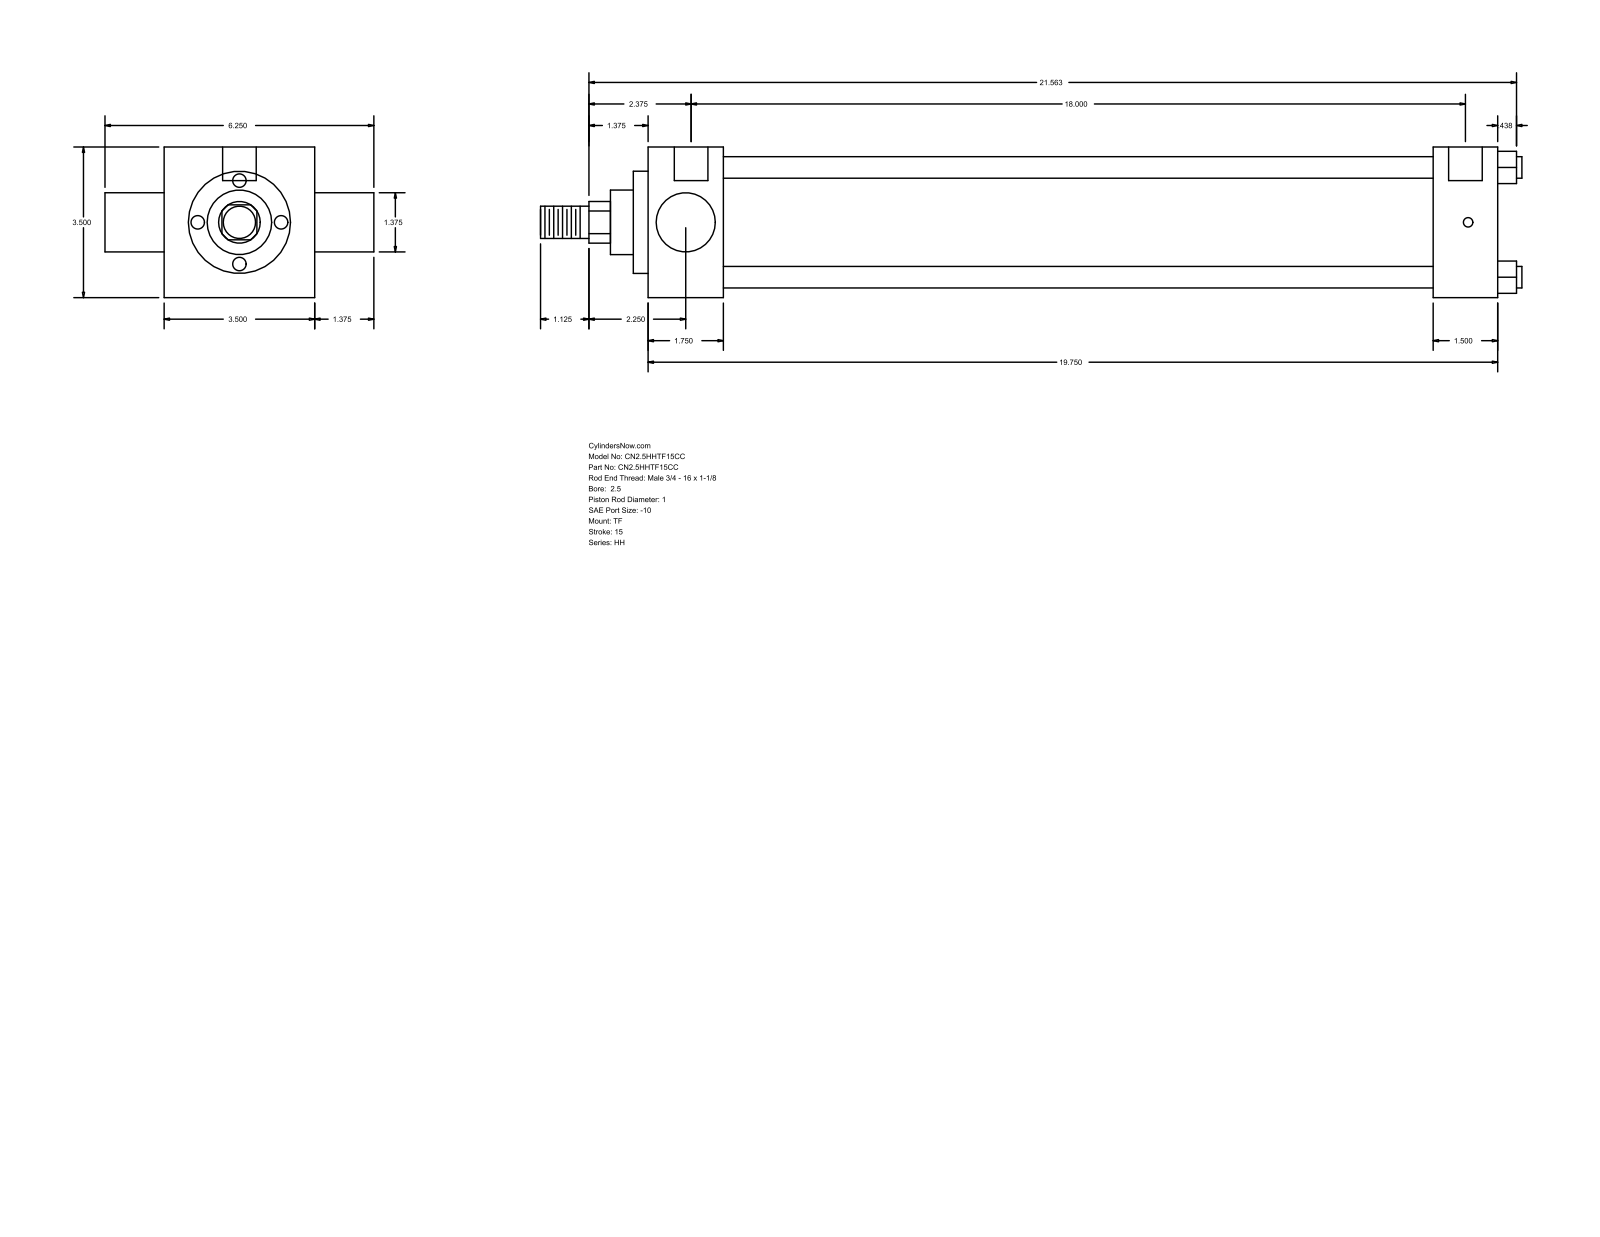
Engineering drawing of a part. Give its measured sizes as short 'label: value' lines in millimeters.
name: HH_TF__0250_1
written by: GSSL Pune (CONFIG_CONTROL_DESIGN)
unit: mm
bodies: 0 solids, 86 faces (61 planar, 25 cylindrical, 0 other)
size: 579.44 × 158.75 × 88.9
holes: 3× ⌀5.56, 2× ⌀19.84
bosses: 4× ⌀12.7, 1× ⌀73.03, 1× ⌀60.33, 1× ⌀38.1, 1× ⌀34.92, 1× ⌀25.4, 1× ⌀19.05
rounds: 1× R12.29
face distances: 88.9, 501.66, 38.1, 44.46, 457.2, 463.56, 419.1, 34.93, 123.83, 8.73
hole spacings: 1.59, 458.78, 457.19, 460.37
